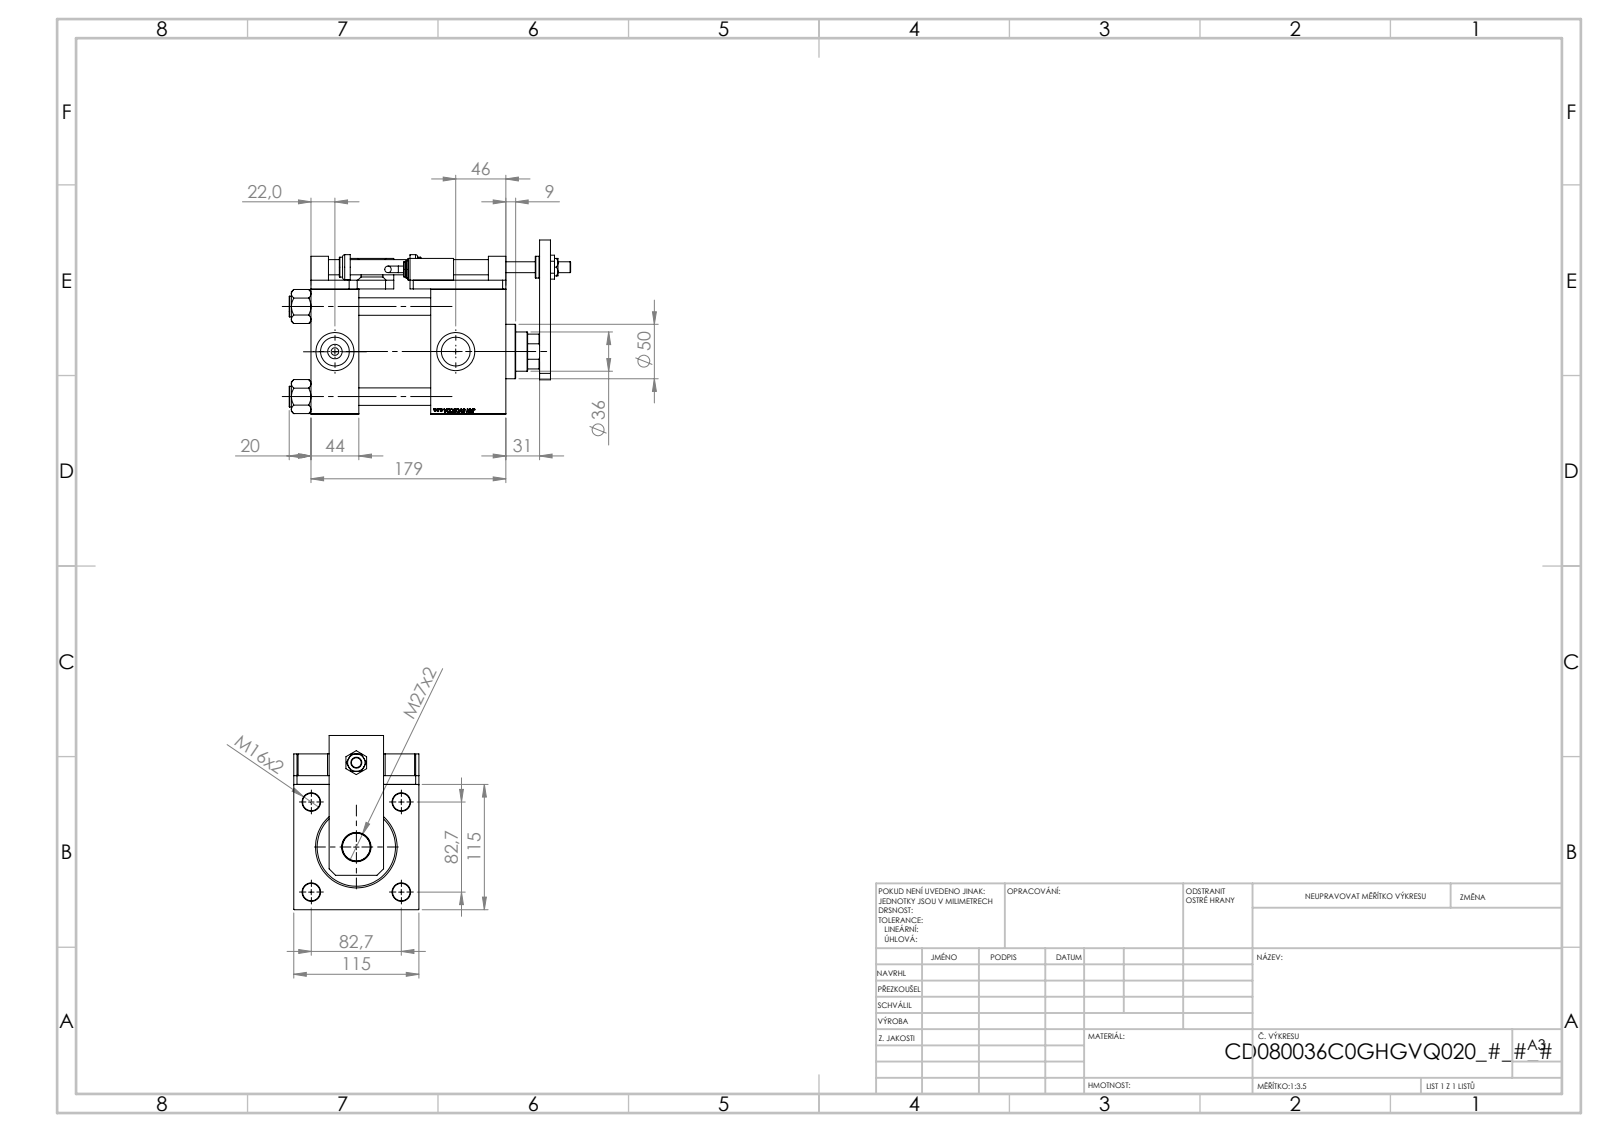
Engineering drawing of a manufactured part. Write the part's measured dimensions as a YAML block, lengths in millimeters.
part_name: "NUT_M5_V215CD_C; V215CD_SWITCH_Q_ZARAZKA; V215CD_SWITCH_Q_PODLOZKA_FRONT; V215CD_SWITCH_Q_DIMA (+7 more)"
step_written_by: "SolidWorks 2019 (CONFIG_CONTROL_DESIGN)"
units: millimeters
bodies: {solids: 24, faces: 1424, planar: 695, cylindrical: 154, other: 575}
overall_size: [258.5, 160, 115]
volume: 2080000
surface_area: 359660
round_holes:
  - {diameter: 8.5, count: 4}
  - {diameter: 13.5, count: 4}
  - {diameter: 16, count: 4}
  - {diameter: 7, count: 2}
  - {diameter: 26.44, count: 2}
  - {diameter: 35, count: 2}
  - {diameter: 10, count: 1}
  - {diameter: 14, count: 1}
  - {diameter: 25.5, count: 1}
  - {diameter: 27, count: 1}
  - {diameter: 36, count: 1}
  - {diameter: 39, count: 1}
round_bosses_or_shafts:
  - {diameter: 19, count: 4}
  - {diameter: 20, count: 3}
  - {diameter: 16, count: 2}
  - {diameter: 14, count: 2}
  - {diameter: 6, count: 2}
  - {diameter: 86, count: 1}
  - {diameter: 50, count: 1}
  - {diameter: 23, count: 1}
partial_cylinders:
  - {radius: 7.5, count: 4}
  - {radius: 17.5, count: 1}
face_to_face_distances: [115, 8, 44, 110, 123, 179, 135, 69, 66, 20]
hole_center_spacings: [58.48, 82.7, 32, 54.92, 116.96, 125.84, 163, 166.11]
